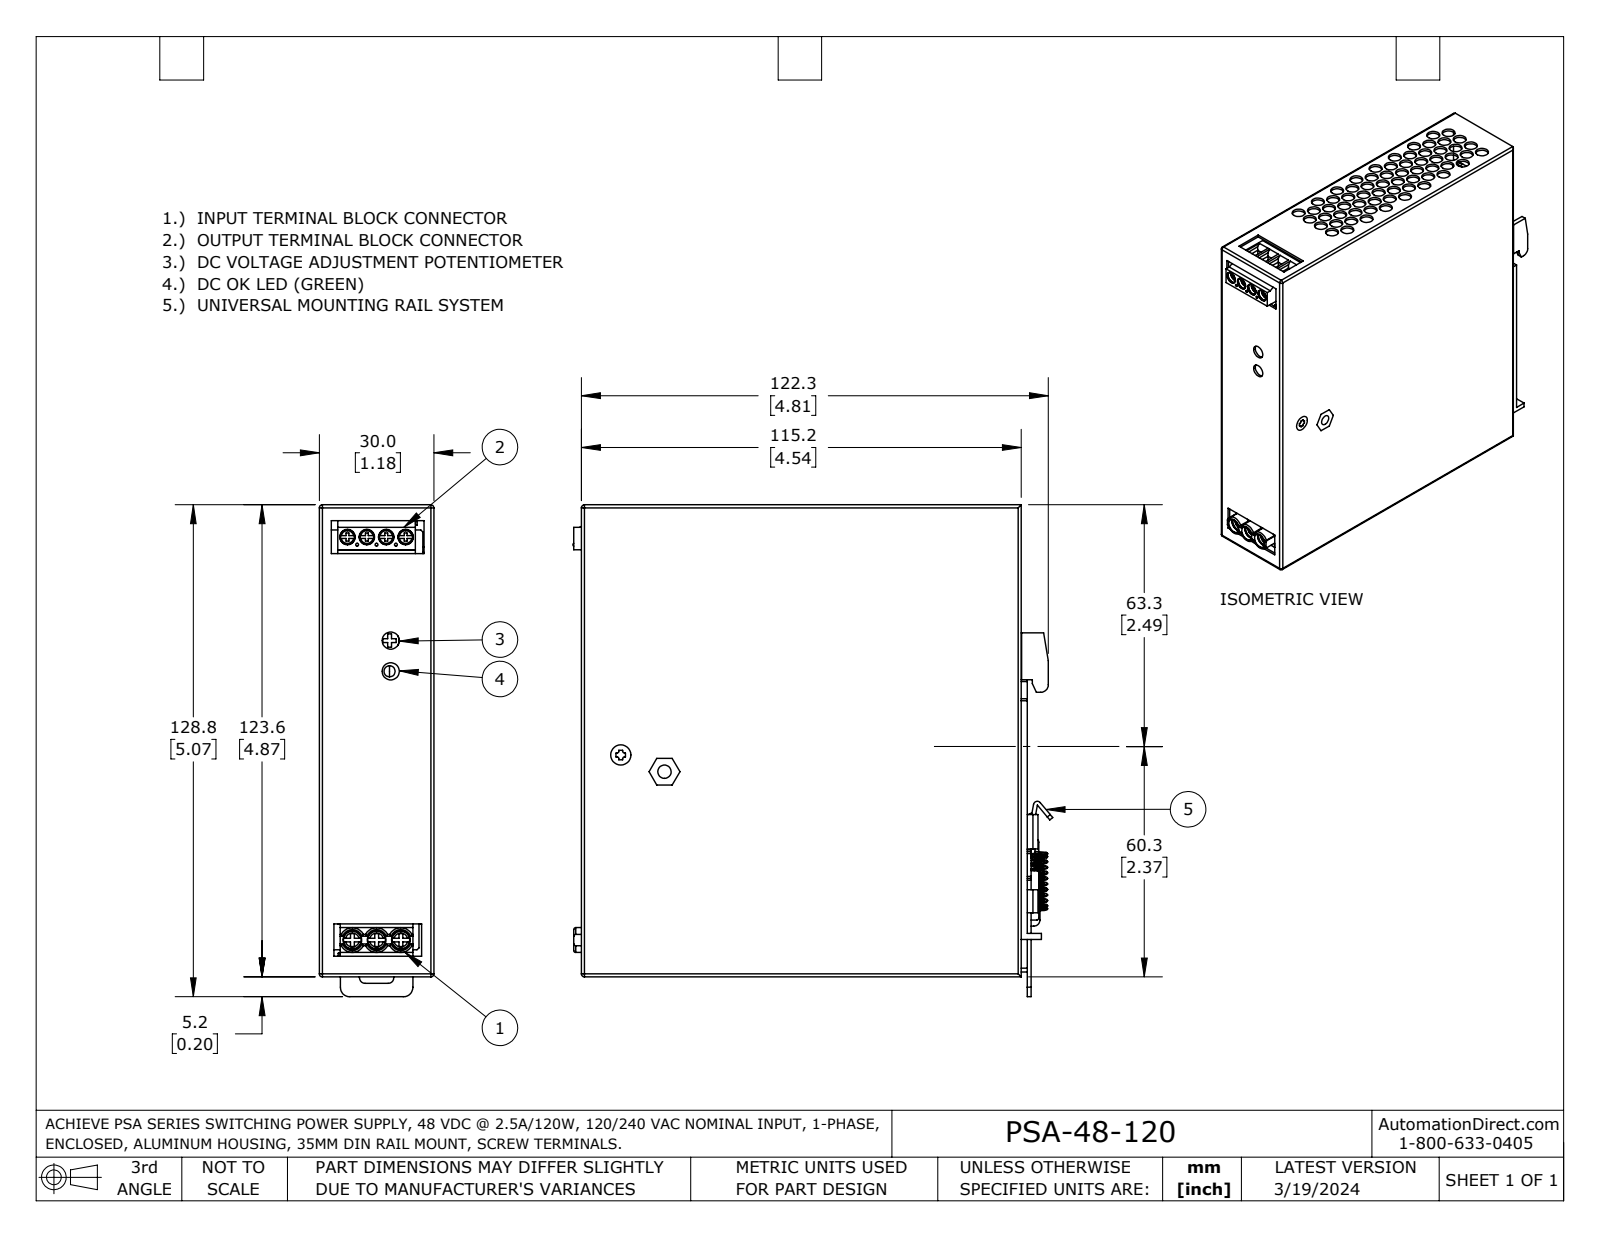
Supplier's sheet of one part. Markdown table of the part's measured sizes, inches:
| quantity | value |
| --- | --- |
| part name | PSA-48-120 |
| STEP written by | SolidWorks 2023 (AUTOMOTIVE_DESIGN) |
| units | inches |
| bodies | 5 solids, 1022 faces (619 planar, 334 cylindrical, 69 other) |
| overall size | 5.071 × 4.949 × 1.181 |
| volume | 2.585 in³ |
| surface area | 137.5 in² |
| round holes (diameter × count) | 0.177 × 69, 0.152 × 4, 0.159 × 4, 0.183 × 3, 0.193 × 3, 0.138 × 2, 0.079 × 1, 0.197 × 1 |
| round bosses / shafts (diameter × count) | 0.156 × 4, 0.15 × 4, 0.184 × 3, 0.118 × 3, 0.023 × 3, 0.039 × 2, 0.114 × 1 |
| partial cylindrical surfaces (radius × count) | 0.02 × 63, 0.004 × 12, 0.039 × 11, 0.031 × 10, 0.063 × 8, 0.059 × 4, 0.128 × 3, 0.098 × 2 |
| main face-to-face distances | 0.031, 1.15, 1.181, 1.118, 4.504, 4.835, 4.472, 0.063, 0.094, 4.866 |
| hole center spacings | 0.432, 0.779, 1.143, 0.374, 0.572, 0.217, 0.748, 1.512 |
